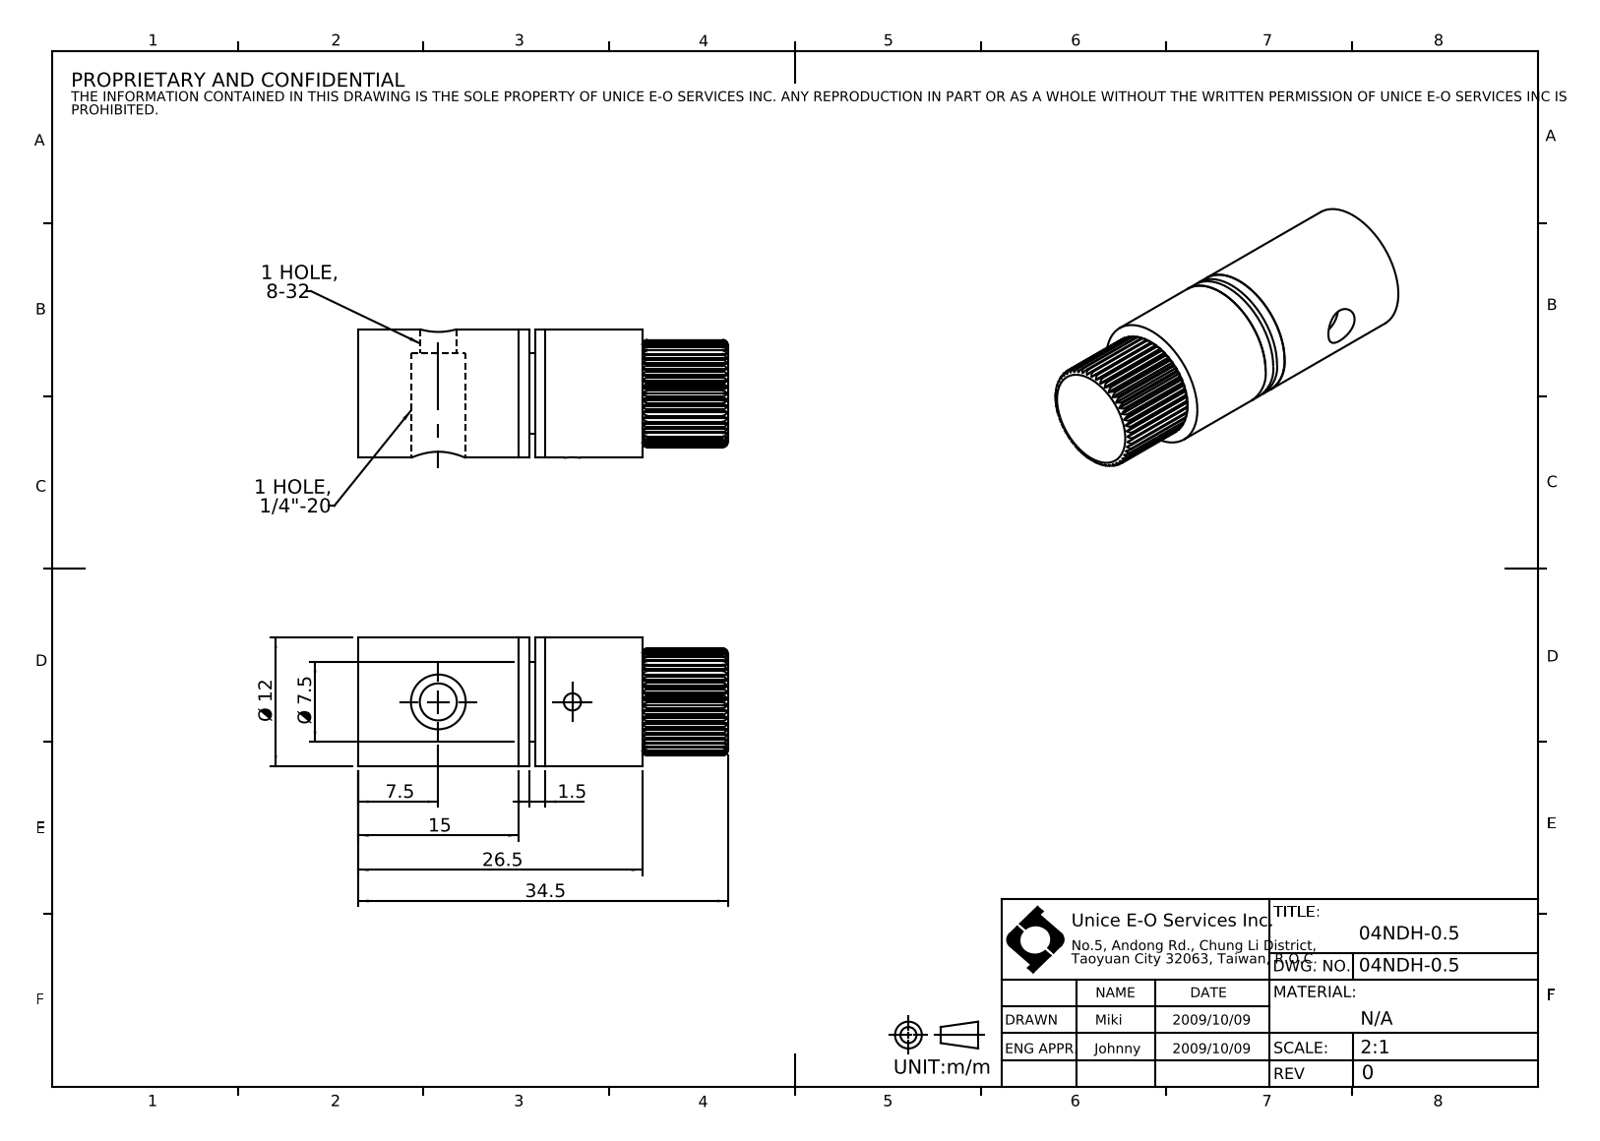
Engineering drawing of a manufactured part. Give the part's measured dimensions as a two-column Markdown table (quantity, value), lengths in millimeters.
| quantity | value |
| --- | --- |
| part name | 04NDH-0.5 |
| STEP written by | SolidWorks 2016 (CONFIG_CONTROL_DESIGN) |
| units | millimeters |
| bodies | 5 solids, 267 faces (117 planar, 142 cylindrical, 8 other) |
| overall size | 34.5 × 12 × 12 |
| volume | 3 329 mm³ |
| surface area | 2 894 mm² |
| round holes (diameter × count) | 1.6 × 1, 3.3 × 1, 3.45 × 1, 4.6 × 1, 5.11 × 1, 7.5 × 1, 7.7 × 1 |
| round bosses / shafts (diameter × count) | 12 × 1, 4 × 1 |
| partial cylindrical surfaces (radius × count) | 1 × 1, 5 × 1 |
| main face-to-face distances | 1, 1.5, 9, 2.5, 11.5, 6.72, 15, 17.5, 26.5, 16.5 |
| hole center spacings | 12.5 |
